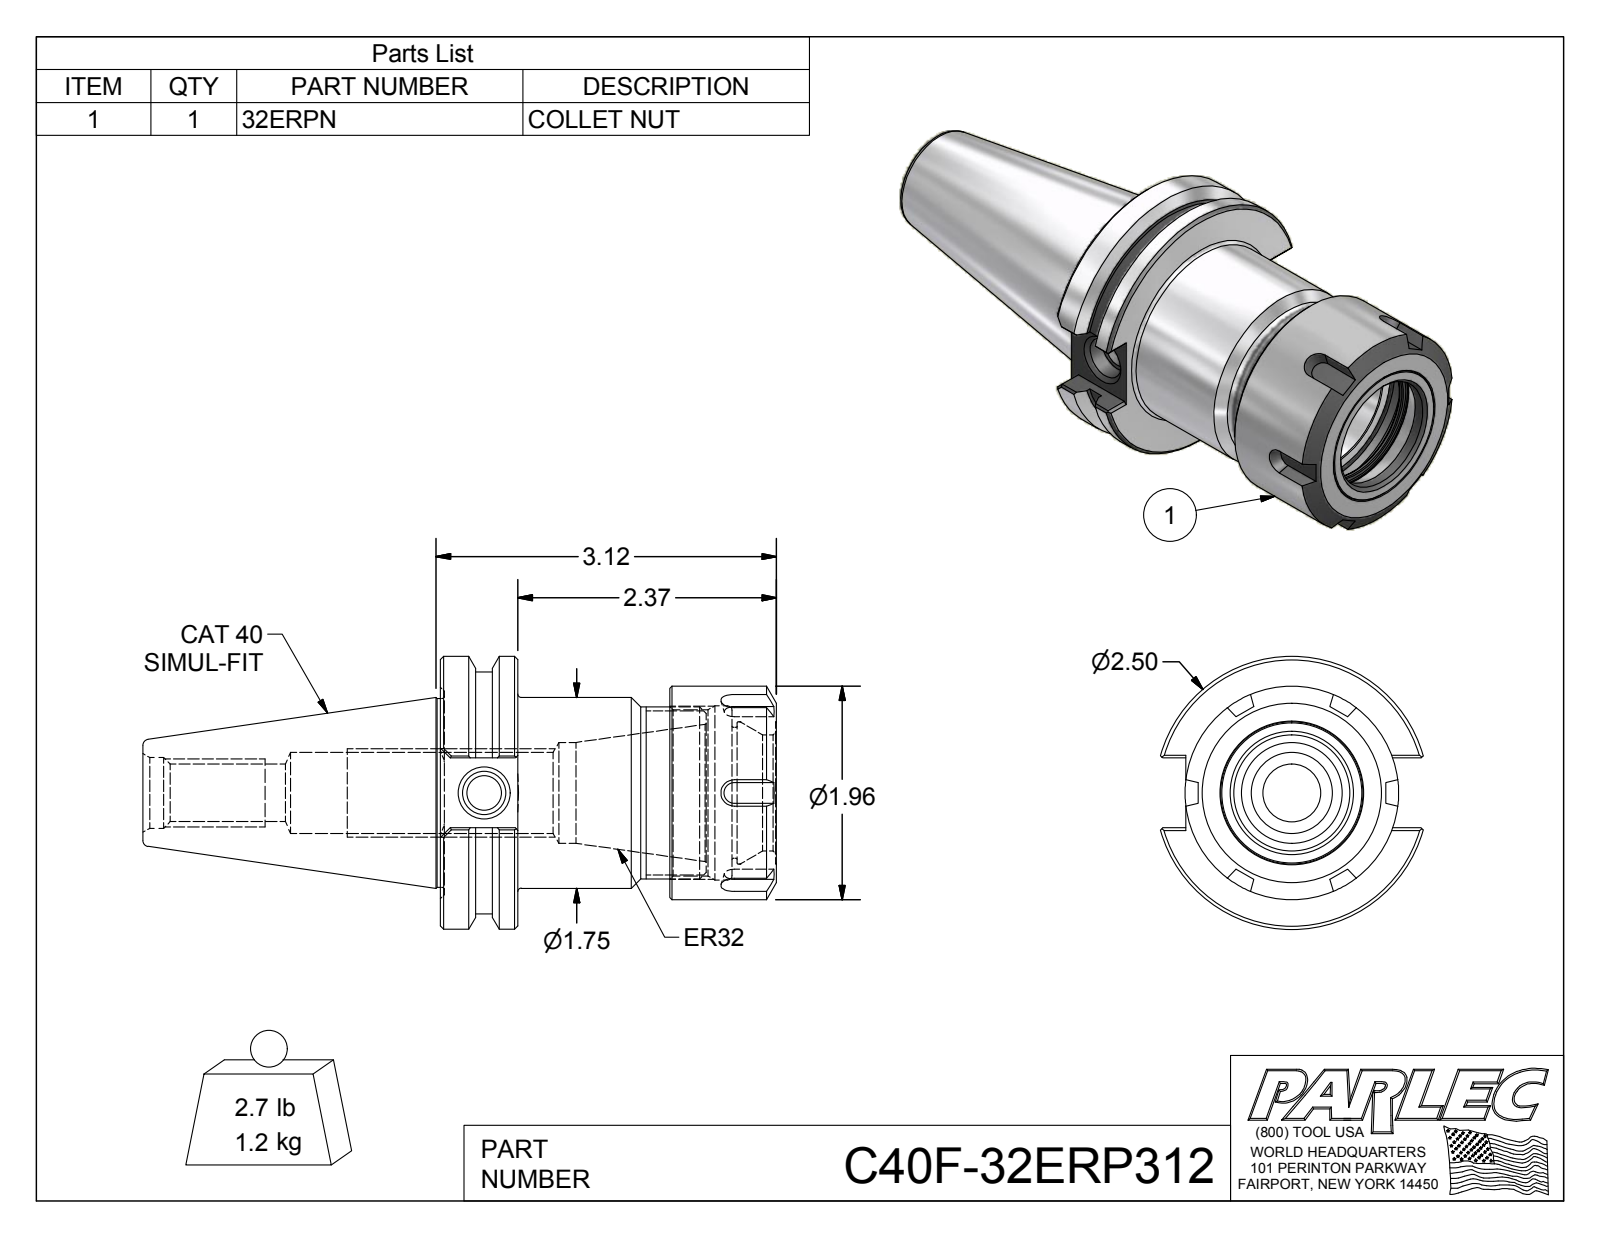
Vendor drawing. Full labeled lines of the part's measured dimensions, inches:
Part name (STEP PRODUCT): C40F-32ERP312; C40F-32ER3-1; 32ERPN
STEP written by: Autodesk Inventor 2012 (AUTOMOTIVE_DESIGN)
Units: inches
Bodies: 2 solids, 123 faces (55 planar, 21 cylindrical, 47 other)
Overall size (bounding box): 5.808 × 2.5 × 2.406
Volume: 9.606 in³ · Surface area: 61.17 in²
Round holes (diameter × count): ⌀0.315 ×1, ⌀0.399 ×1, ⌀0.527 ×1, ⌀0.648 ×1, ⌀0.745 ×1, ⌀0.925 ×1, ⌀1.063 ×1, ⌀1.2 ×1, ⌀1.305 ×1, ⌀1.523 ×1, ⌀1.595 ×1
Round bosses / shafts (diameter × count): ⌀2.5 ×1, ⌀2.215 ×1, ⌀1.958 ×1, ⌀1.75 ×1, ⌀1.73 ×1, ⌀1.575 ×1
Main face-to-face distances: 0.711, 3.081, 2.37, 2.103, 1.392, 0.978, 2.674, 1.963, 0.571, 0.407
